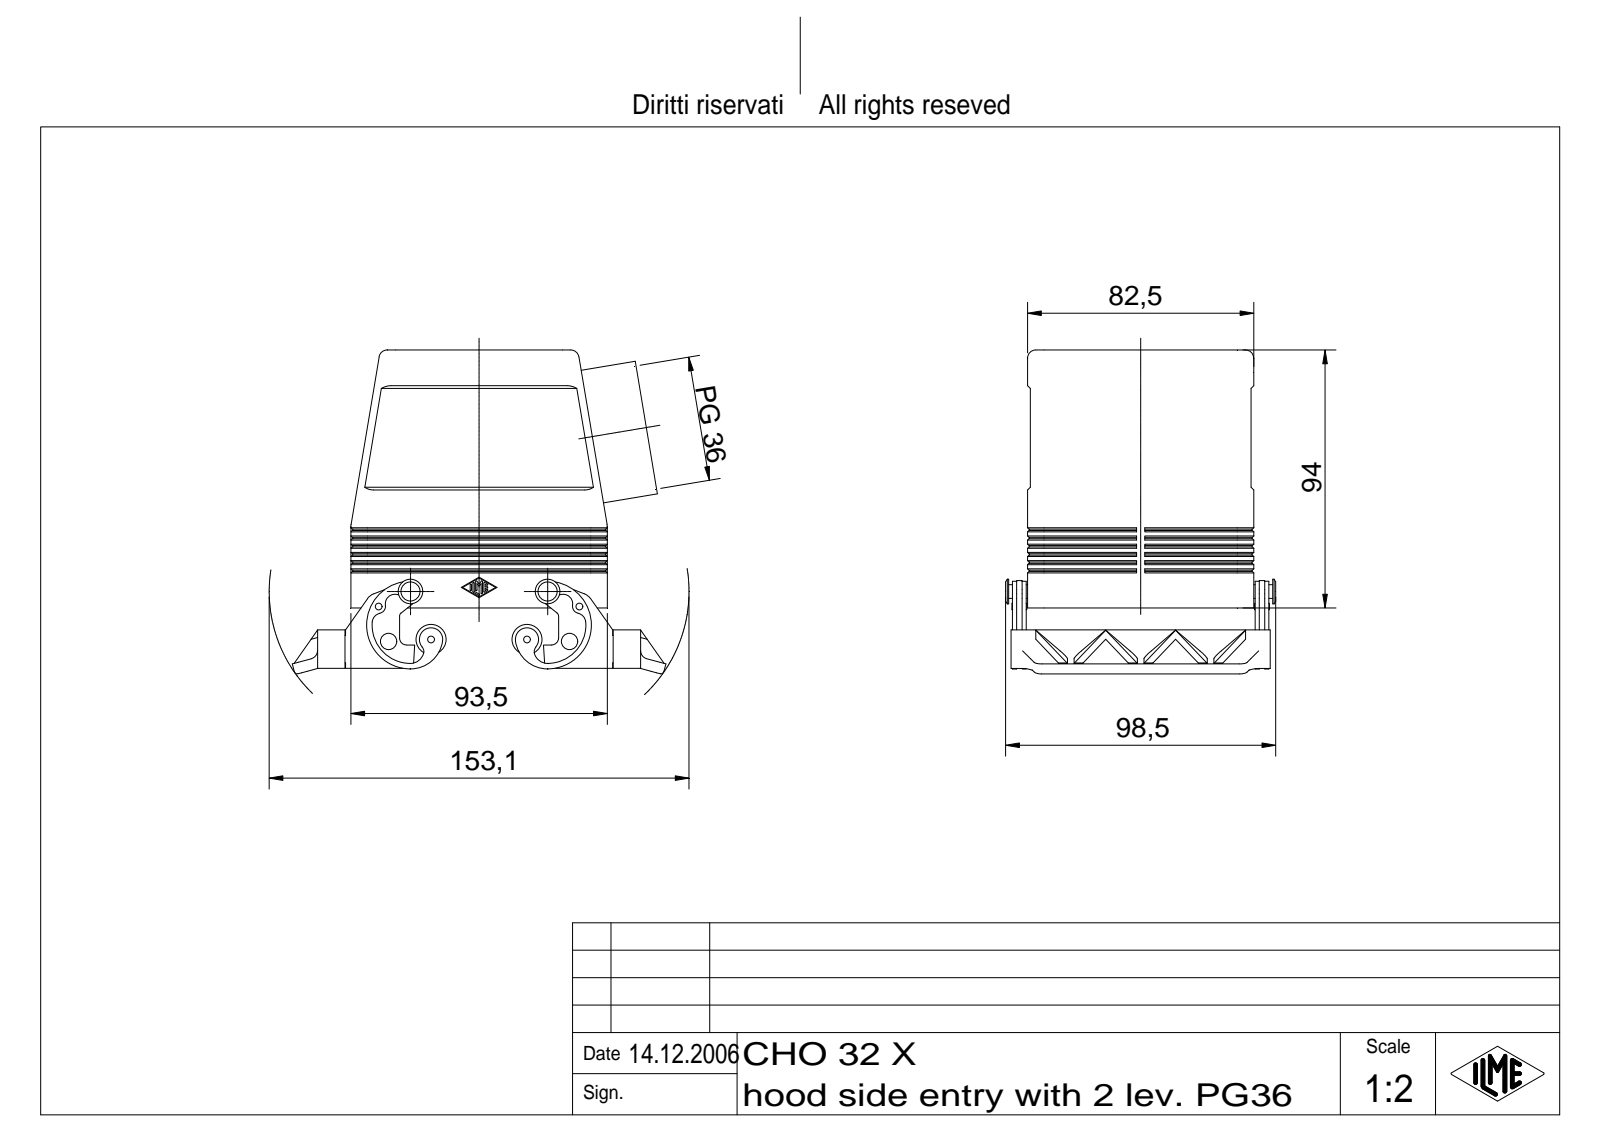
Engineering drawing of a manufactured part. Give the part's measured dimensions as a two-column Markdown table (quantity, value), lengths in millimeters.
| quantity | value |
| --- | --- |
| part name | CHO 32 X |
| STEP written by | Autodesk Inventor 7 (AUTOMOTIVE_DESIGN) |
| units | millimeters |
| bodies | 1 solid, 1067 faces (318 planar, 286 cylindrical, 463 other) |
| overall size | 136.28 × 118.03 × 98.5 |
| volume | 174 738 mm³ |
| surface area | 99 927 mm² |
| round holes (diameter × count) | 2.46 × 4, 3.5 × 4, 2.5 × 2, 6 × 2, 43.48 × 1, 45.48 × 1 |
| round bosses / shafts (diameter × count) | 11 × 2, 9 × 2, 5 × 2, 2 × 2, 49 × 1 |
| partial cylindrical surfaces (radius × count) | 0.25 × 14, 3 × 14, 2 × 12, 6 × 10, 1 × 6, 2.5 × 6, 3.5 × 4, 5 × 4 |
| main face-to-face distances | 4, 82.5, 78.5, 74.5, 3, 11, 1, 77.5, 81.5, 71.5 |
| hole center spacings | 13.21, 27, 70.75, 77.5, 82.07, 66, 73.2 |
